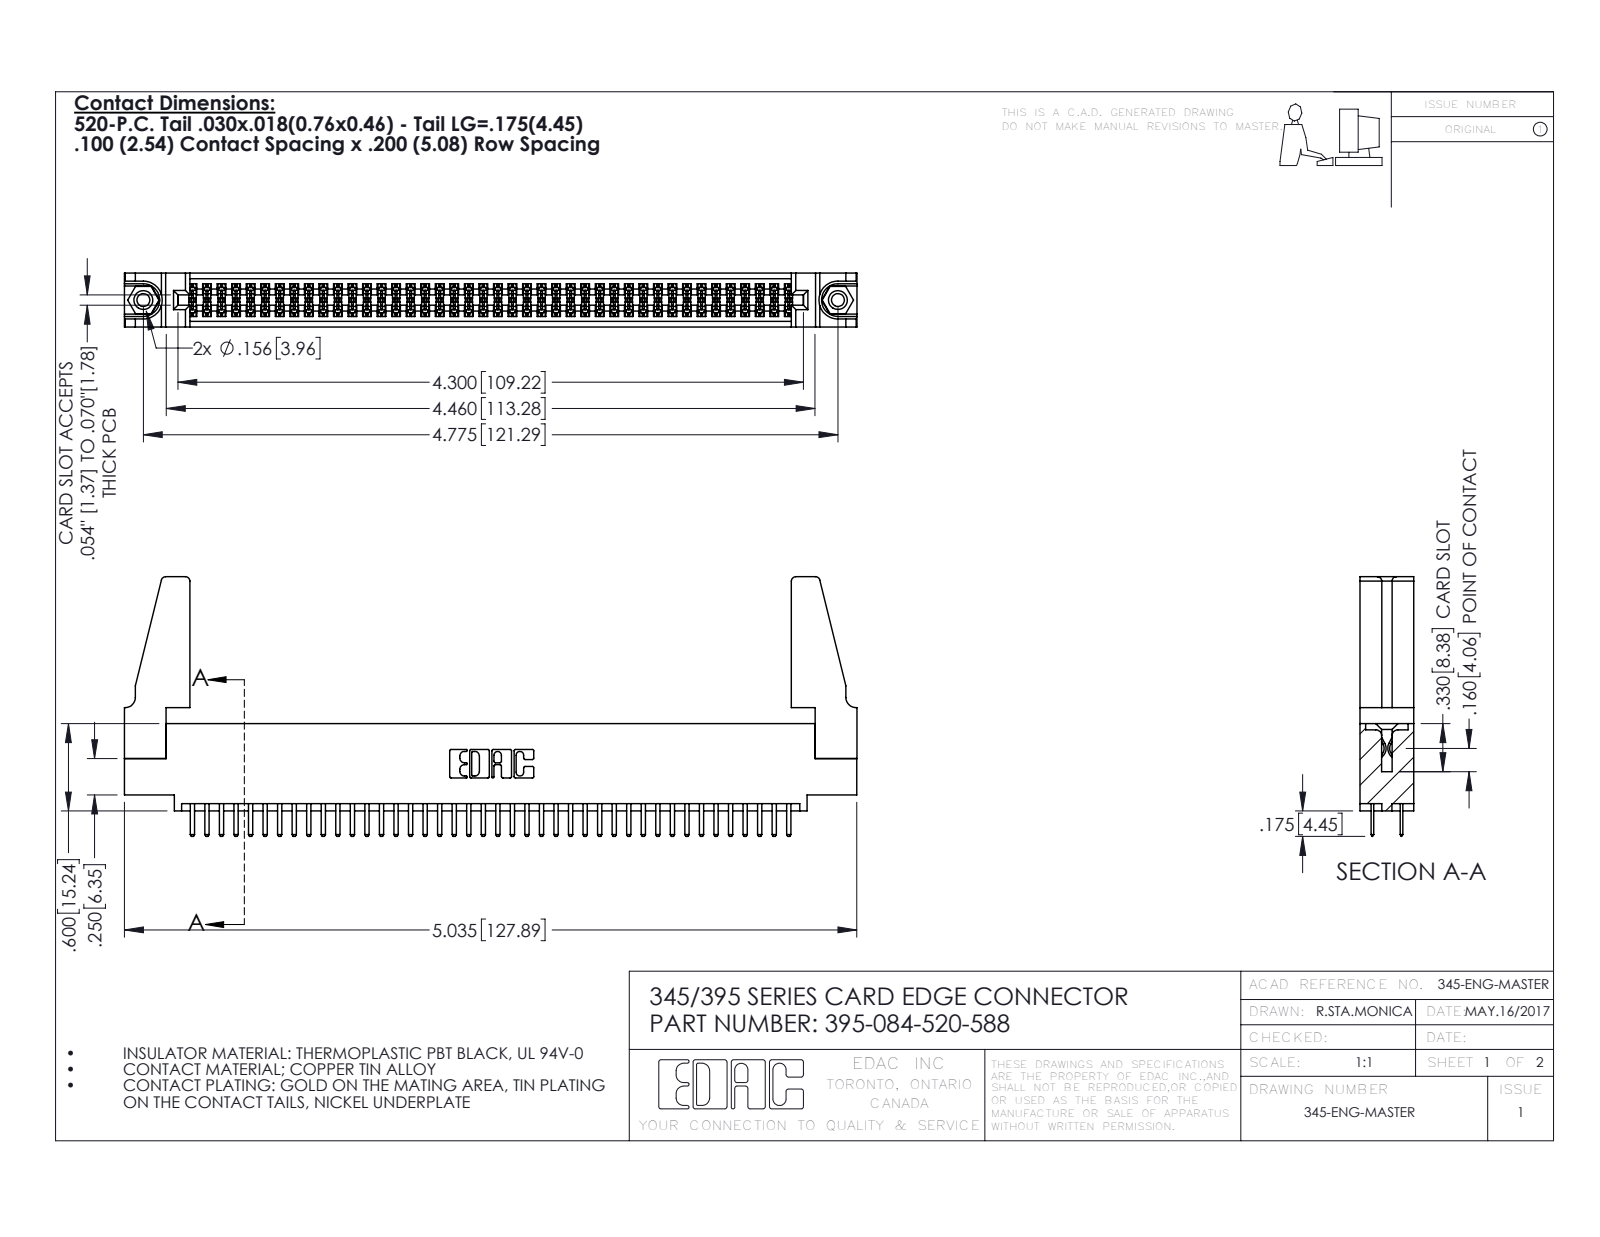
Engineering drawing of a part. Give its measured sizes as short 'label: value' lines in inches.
name: 345-250-001_345-250-001-102; 395-084-520-588; 345-220-078_345-220-088; 345-292-001_345-293-120 (+1 more)
written by: SolidWorks 2016 (CONFIG_CONTROL_DESIGN)
unit: in
bodies: 89 solids, 4790 faces (3096 planar, 1678 cylindrical, 16 other)
size: 5.036 × 1.785 × 0.37
volume: 0.95 in³; area: 33.08 in²
holes: 2× ⌀0.089, 2× ⌀0.125, 2× ⌀0.156, 1× ⌀0.064
bosses: 2× ⌀0.155
rounds: 126× R0.006, 88× R0.01, 22× R0.01, 8× R0.03, 6× R0.007, 6× R0.031, 3× R0.026, 2× R0.014
face distances: 0.072, 0.298, 0.37, 0.2, 0.098, 0.272, 0.025, 0.225, 0.022, 0.072
hole spacings: 0.27, 4.539, 4.775
